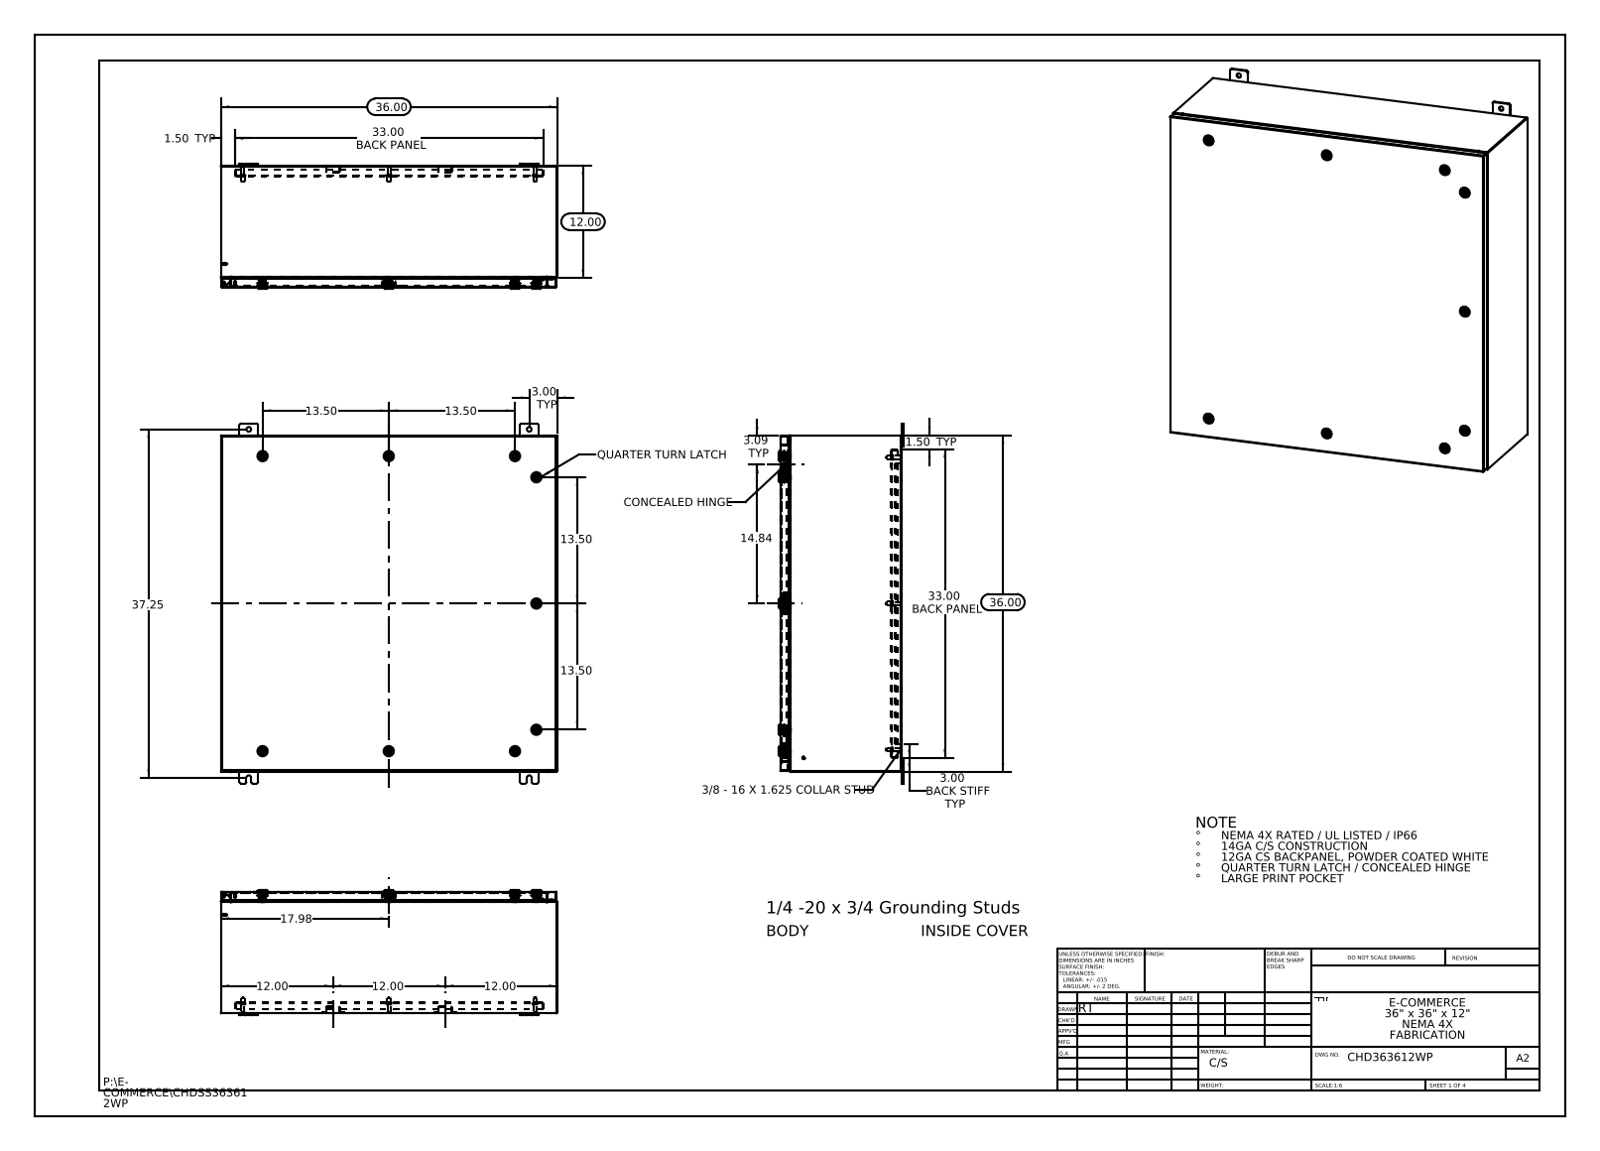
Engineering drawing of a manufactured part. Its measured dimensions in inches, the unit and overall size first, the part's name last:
Units: inches
Overall size (bounding box): 38.5 × 36 × 13.356
Round holes (diameter × count): ⌀0.5 ×12, ⌀0.197 ×9, ⌀0.394 ×9, ⌀0.4 ×9, ⌀0.63 ×9, ⌀0.787 ×9, ⌀0.136 ×6, ⌀0.25 ×6, ⌀0.211 ×1
Round bosses / shafts (diameter × count): ⌀0.236 ×11, ⌀1.102 ×9, ⌀0.78 ×9, ⌀0.626 ×9, ⌀0.61 ×9, ⌀0.531 ×9, ⌀0.392 ×9, ⌀0.114 ×9
Partial cylindrical surfaces — rounded edges, fillets, slot ends (radius × count): R0.006 ×297, R0.118 ×297, R0.028 ×108, R0.02 ×36, R0.197 ×36, R0.013 ×34, R0.088 ×30, R0.19 ×24
Main face-to-face distances: 0.075, 35.925, 0.074, 12.861, 12.936, 13.01, 12.935, 0.104, 1, 1.075
Hole centre spacings: 13.5, 15.625, 14, 14.176, 22.097, 34.317, 34.939, 34.939
Volume: 508.9 in³ · Surface area: 12 690 in²
Bodies: 88 solids, 8248 faces (2412 planar, 2574 cylindrical, 3262 other)
Part name (STEP PRODUCT): Concealed Hinge (Cover Side); CHDSS363612WP Mounting Feet; CHDSS363612WP Enclosure Stiffener; Quarter-20 CD Stud (+8 more)
STEP written by: SolidWorks 2013 (CONFIG_CONTROL_DESIGN)
